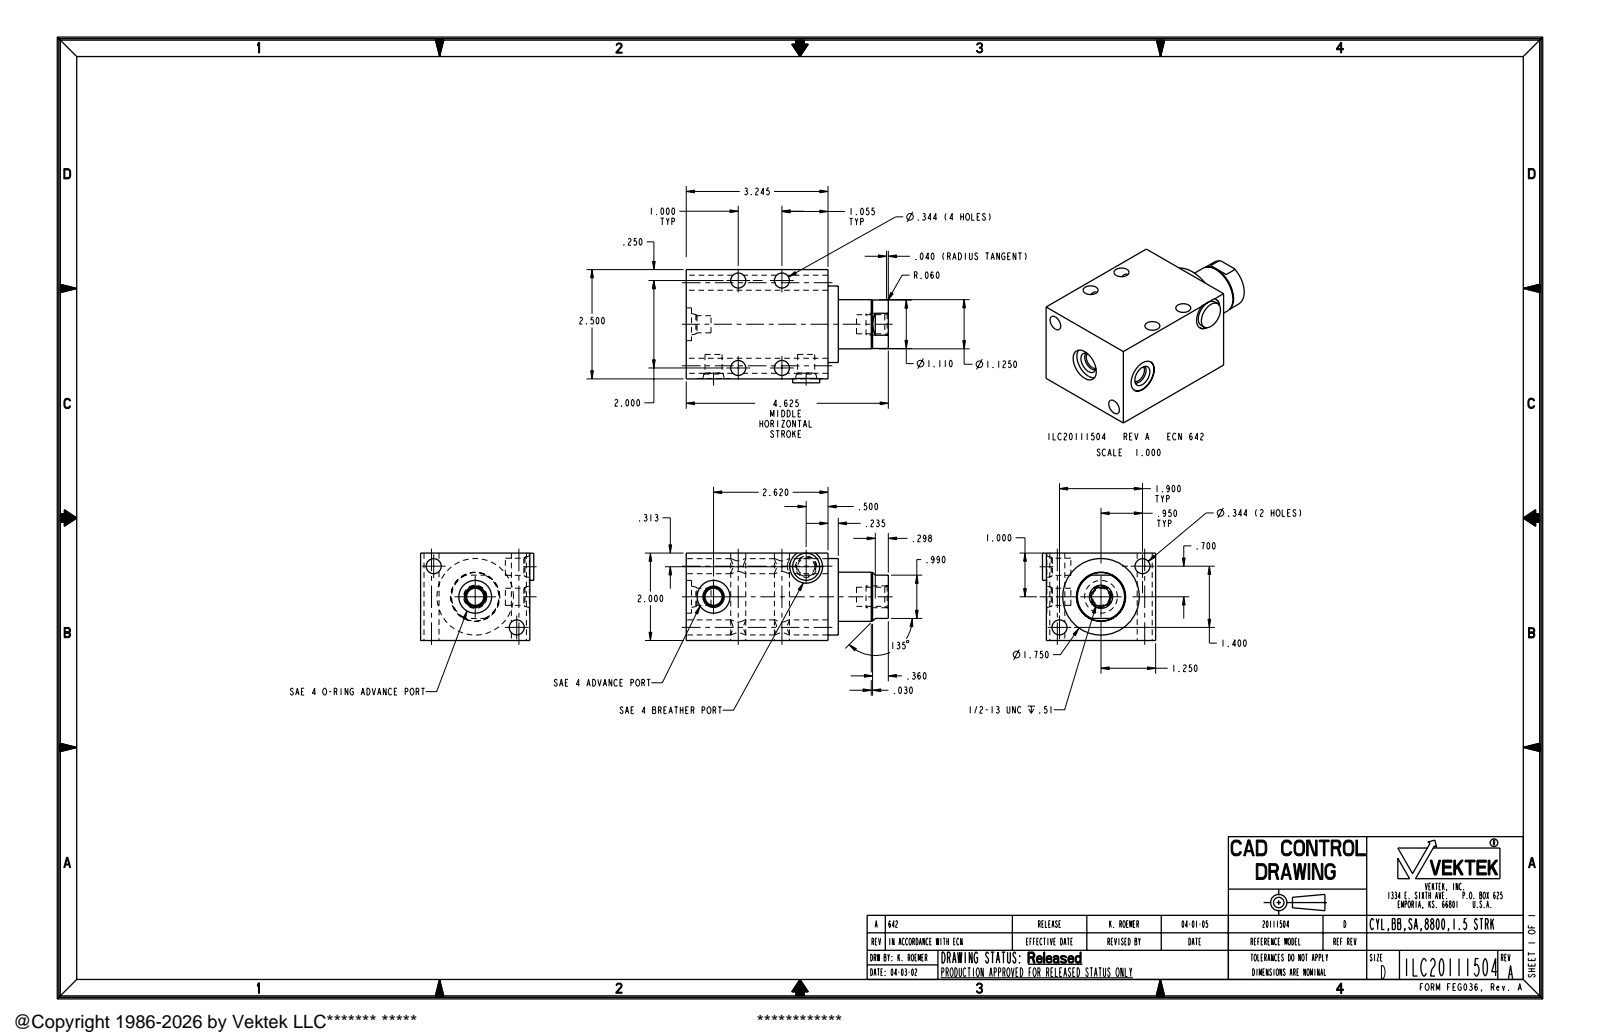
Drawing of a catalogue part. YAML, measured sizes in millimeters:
part_name: "ILC20111504"
step_written_by: "PRO/ENGINEER BY PARAMETRIC TECHNOLOGY CORPORATION, 2004290 (AUTOMOTIVE_DESIGN_CC2)"
units: millimeters
bodies: {solids: 1, faces: 83, planar: 22, cylindrical: 43, other: 18}
overall_size: [117.5, 65.8, 50.8]
volume: 267300
surface_area: 39780
round_holes:
  - {diameter: 8.7, count: 6}
  - {diameter: 10, count: 3}
  - {diameter: 19.1, count: 3}
  - {diameter: 11.1, count: 1}
round_bosses_or_shafts:
  - {diameter: 44.5, count: 1}
  - {diameter: 28.6, count: 1}
  - {diameter: 28.2, count: 1}
  - {diameter: 15.7, count: 1}
  - {diameter: 12.7, count: 1}
face_to_face_distances: [50.8, 63.5, 82.4, 6, 88.4, 29.1, 35.1, 117.5, 63.2, 2.3]
hole_center_spacings: [25.4, 30, 50.8, 56.8, 56.6, 59.9]
